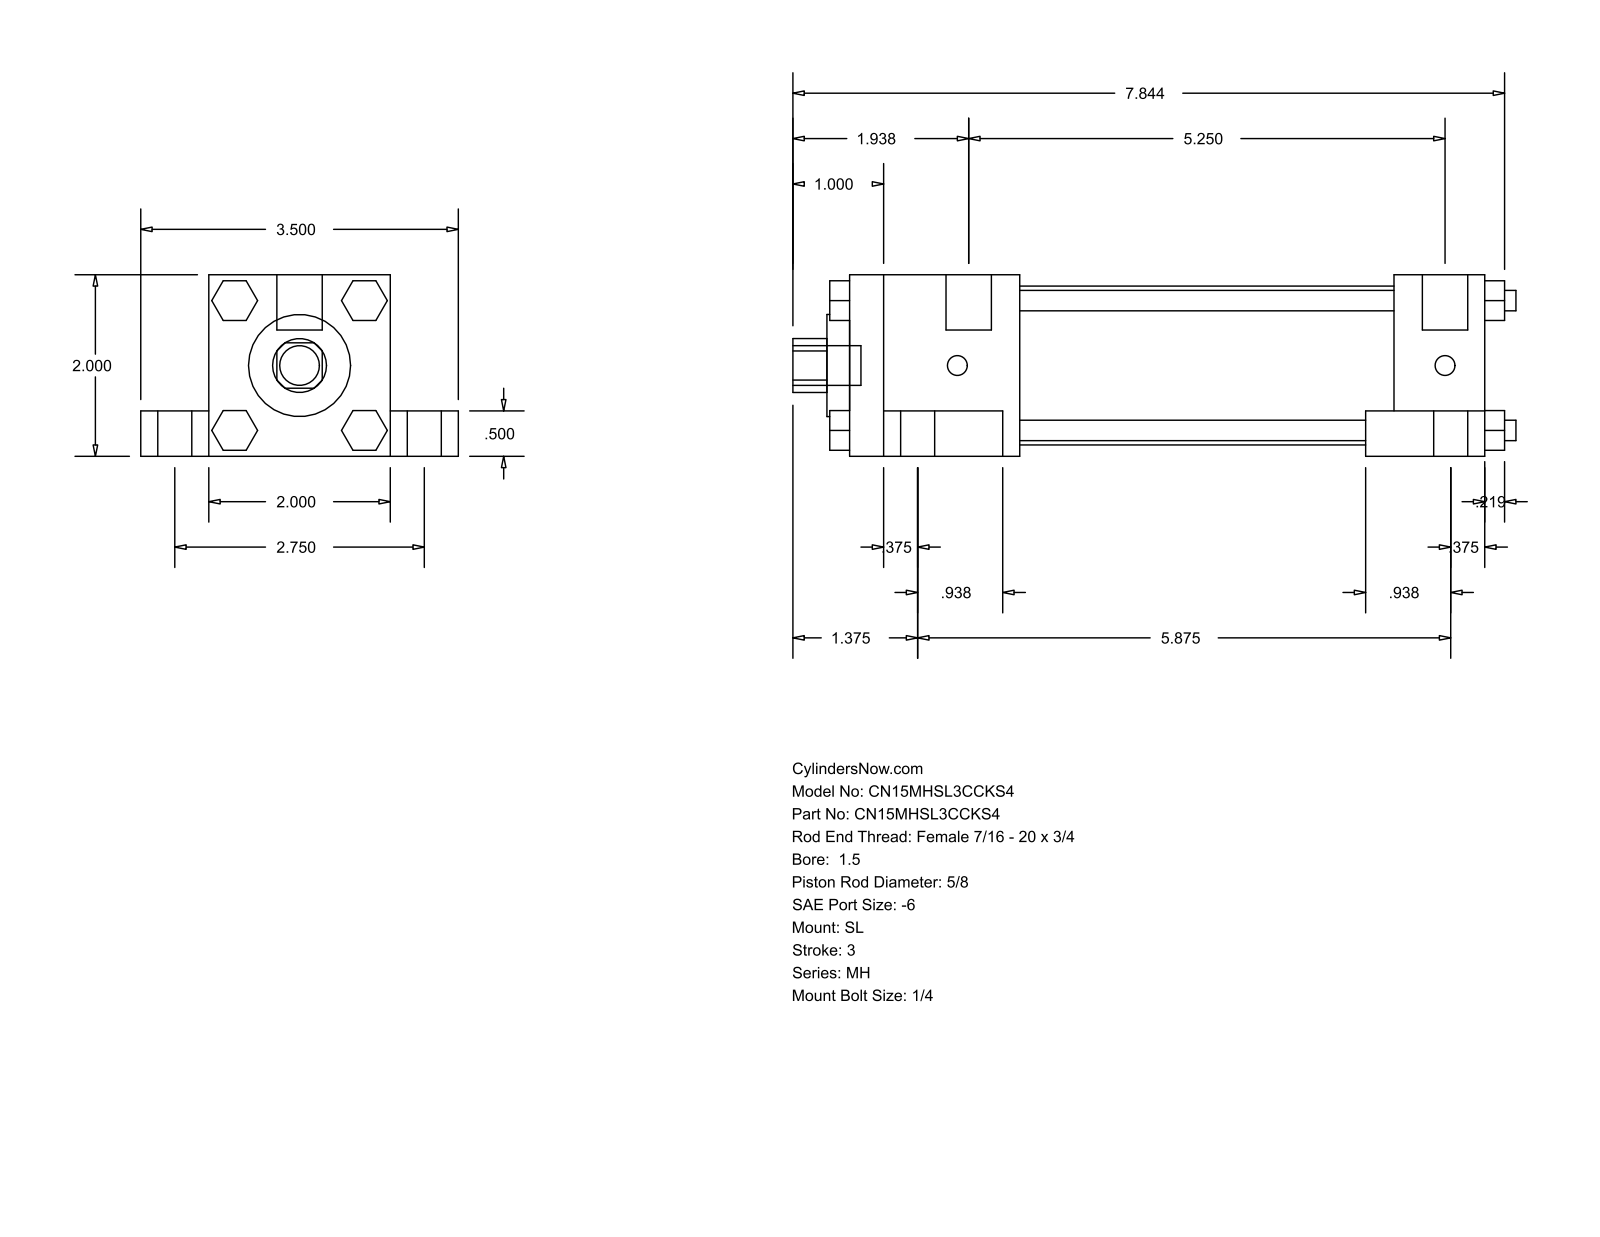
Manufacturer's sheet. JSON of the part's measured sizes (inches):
{"part_name": "MH_SL__0150_0.625", "step_written_by": "GSSL Pune (CONFIG_CONTROL_DESIGN)", "units": "inches", "bodies": {"solids": 0, "faces": 148, "planar": 112, "cylindrical": 36, "other": 0}, "overall_size": [7.969, 3.5, 2], "round_holes": [[0.625, 1], [1.125, 1], [1.75, 1]], "round_bosses_or_shafts": [[0.625, 4], [0.375, 4], [0.225, 4], [0.219, 4], [0.5, 2], [0.437, 1]], "partial_cylinders_radius": [[0.297, 1]], "face_to_face_distances": [2, 1.5, 0.75, 0.5, 2.75, 7, 0.375, 1, 1.313, 5.313]}
